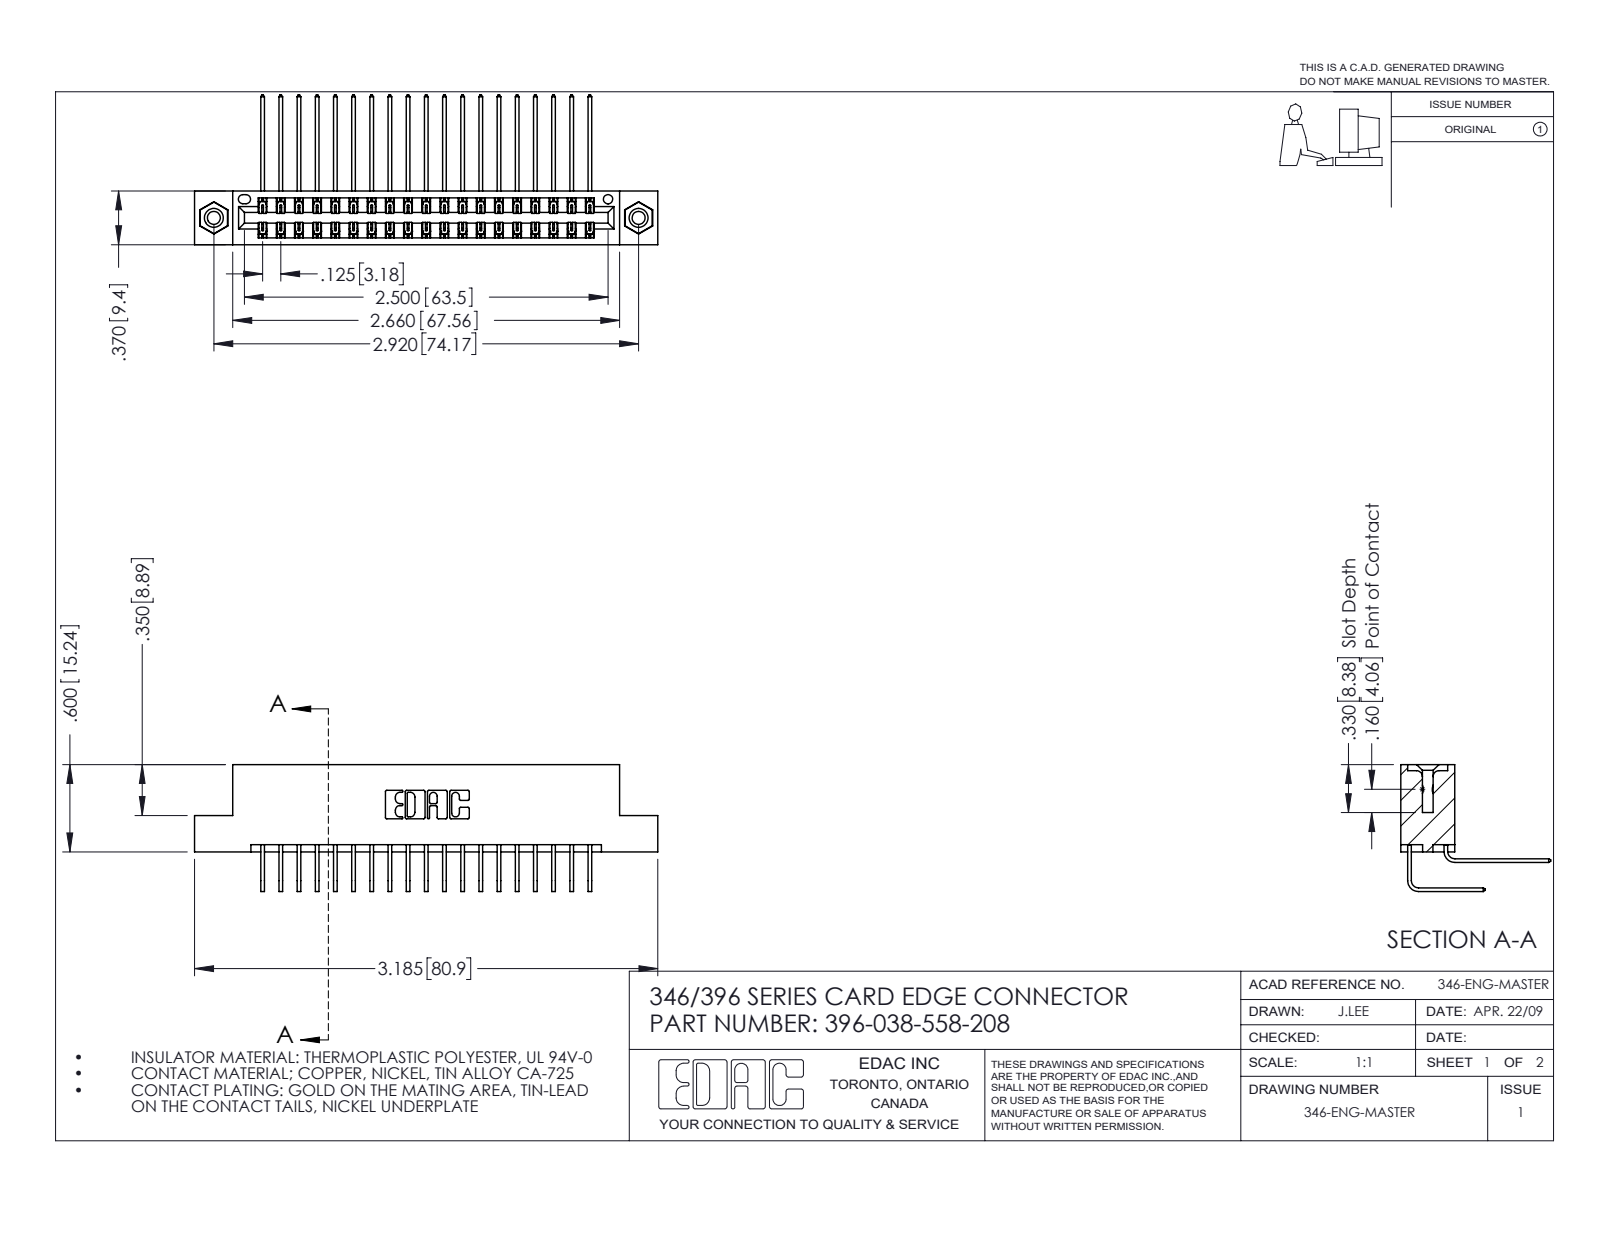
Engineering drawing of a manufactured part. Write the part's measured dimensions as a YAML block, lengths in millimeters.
part_name: "345-292-001_558 559 Tail - 1; 345-292-001_558 Tail - 2; 396-038-558-208; 346 Part_Flush Mounting Lugs - 0.156 Dia-TI (+1 more)"
step_written_by: "SolidWorks 2016 (CONFIG_CONTROL_DESIGN)"
units: millimeters
bodies: {solids: 41, faces: 2234, planar: 1514, cylindrical: 704, other: 16}
overall_size: [80.9, 26.2, 22.2]
volume: 7910
surface_area: 11600
round_holes:
  - {diameter: 2.3, count: 2}
  - {diameter: 3.2, count: 2}
  - {diameter: 4, count: 2}
  - {diameter: 1.6, count: 1}
round_bosses_or_shafts:
  - {diameter: 3.9, count: 2}
partial_cylinders:
  - {radius: 0.2, count: 57}
  - {radius: 0.3, count: 22}
  - {radius: 0.2, count: 6}
  - {radius: 0.8, count: 6}
  - {radius: 0.7, count: 3}
  - {radius: 0.4, count: 2}
  - {radius: 0.6, count: 2}
  - {radius: 0.6, count: 2}
face_to_face_distances: [8.2, 1.2, 6.4, 0.6, 9.4, 7.6, 1.8, 7, 3.8, 5.6]
hole_center_spacings: [6.2, 68.9, 74.2]
